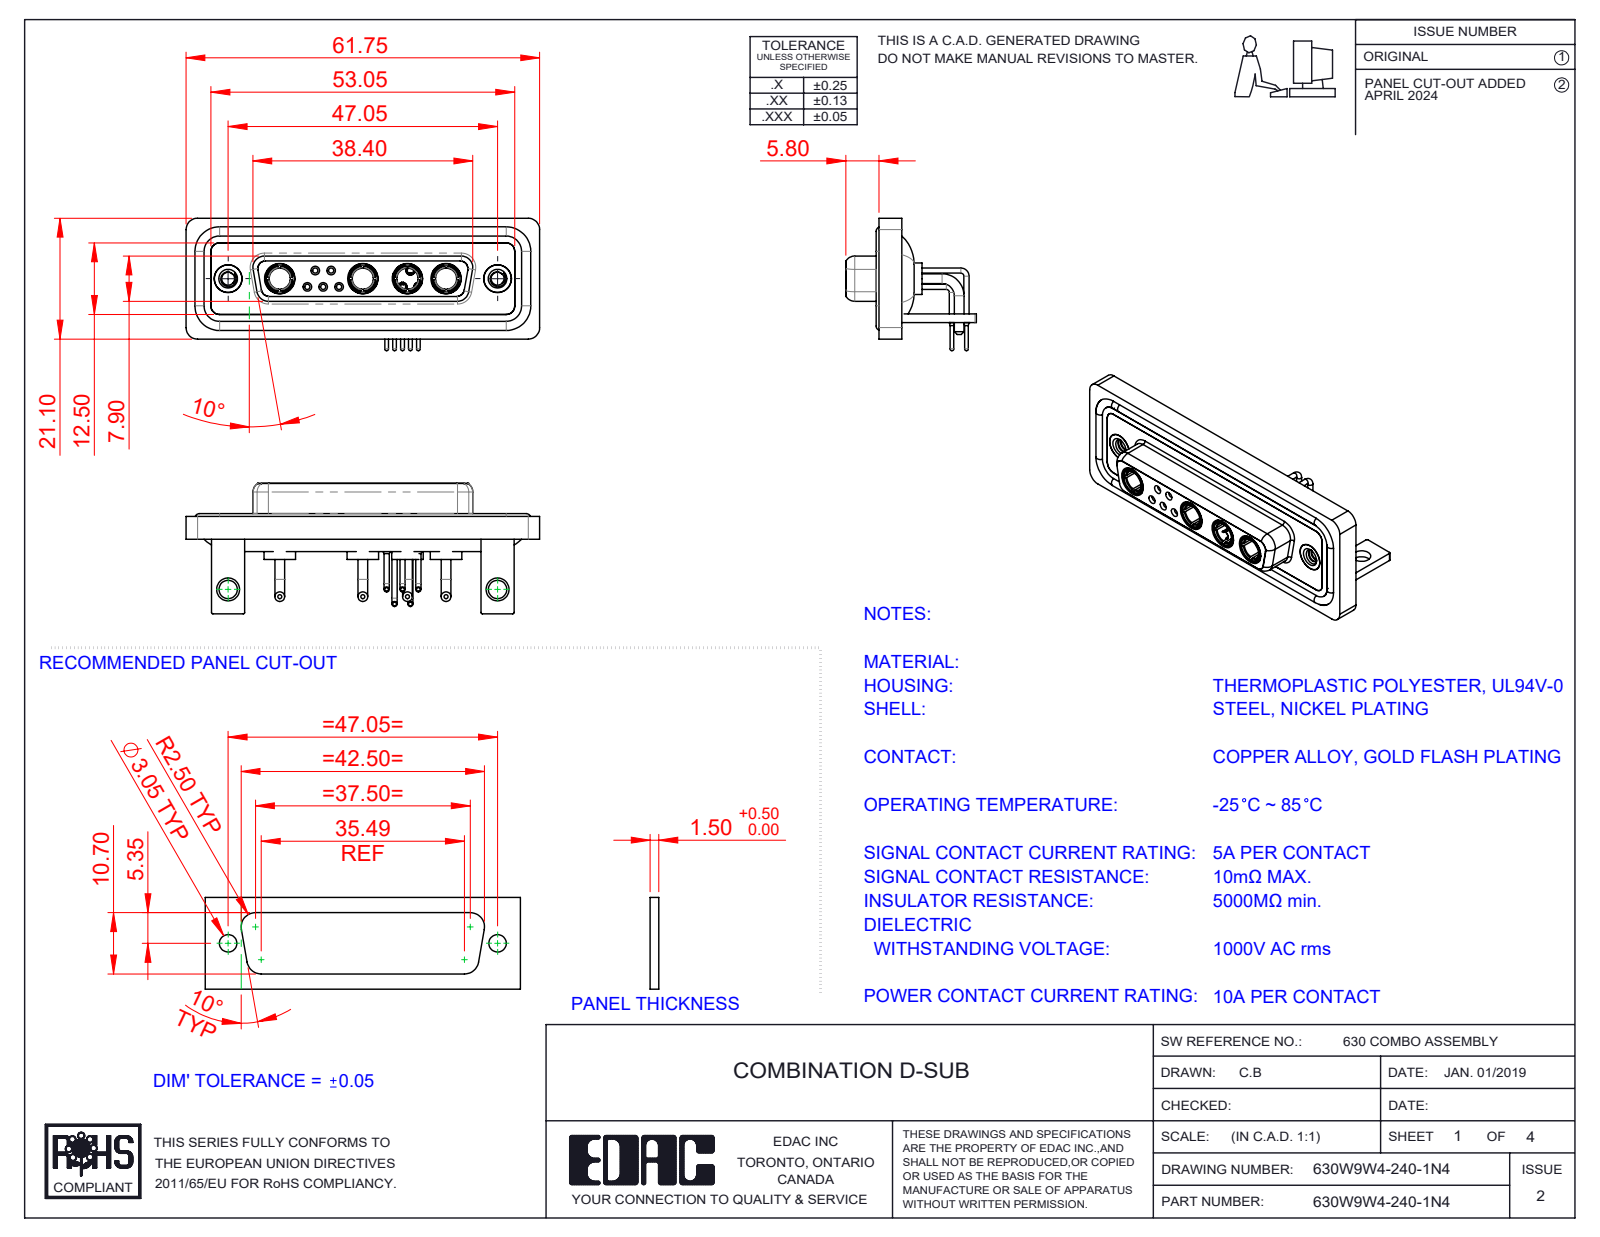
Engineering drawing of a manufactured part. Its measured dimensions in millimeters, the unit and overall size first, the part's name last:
Units: millimetres
Overall size (bounding box): 61.75 × 23.12 × 22.8
Round holes (diameter × count): ⌀4.85 ×6, ⌀0.9 ×5, ⌀1.1 ×5, ⌀1.5 ×5, ⌀2 ×5, ⌀3.7 ×4, ⌀5.3 ×4, ⌀1.6 ×3, ⌀1.7 ×2, ⌀2.26 ×2, ⌀3.2 ×2, ⌀4 ×2
Round bosses / shafts (diameter × count): ⌀0.9 ×10, ⌀1.6 ×9, ⌀1.7 ×8, ⌀2 ×5, ⌀1.5 ×5, ⌀0.65 ×5, ⌀5.5 ×4, ⌀5.2 ×4
Partial cylindrical surfaces — rounded edges, fillets, slot ends (radius × count): R2 ×19, R1.5 ×18, R0.25 ×16, R1.35 ×8, R1.6 ×8, R0.5 ×5, R0.6 ×4, R0.65 ×4
Main face-to-face distances: 0.4, 1.8, 2.9, 3.7, 1.5, 4.1, 1.1, 1.4, 1.6, 2.5
Hole centre spacings: 3.16, 2.77, 5.04, 13.85, 11.08, 12.79, 15.5, 5.54
Volume: 8 587 mm³ · Surface area: 14 579 mm²
Bodies: 22 solids, 1011 faces (316 planar, 427 cylindrical, 268 other)
Part name (STEP PRODUCT): 630Combo Threaded Rivet_2; Power Socket_10A RA; 630Combo Stabilizer Bracket_50 Contacts; 630Combo Contact Row 2_50 Contacts (+6 more)
STEP written by: SolidWorks 2023 (CONFIG_CONTROL_DESIGN)
